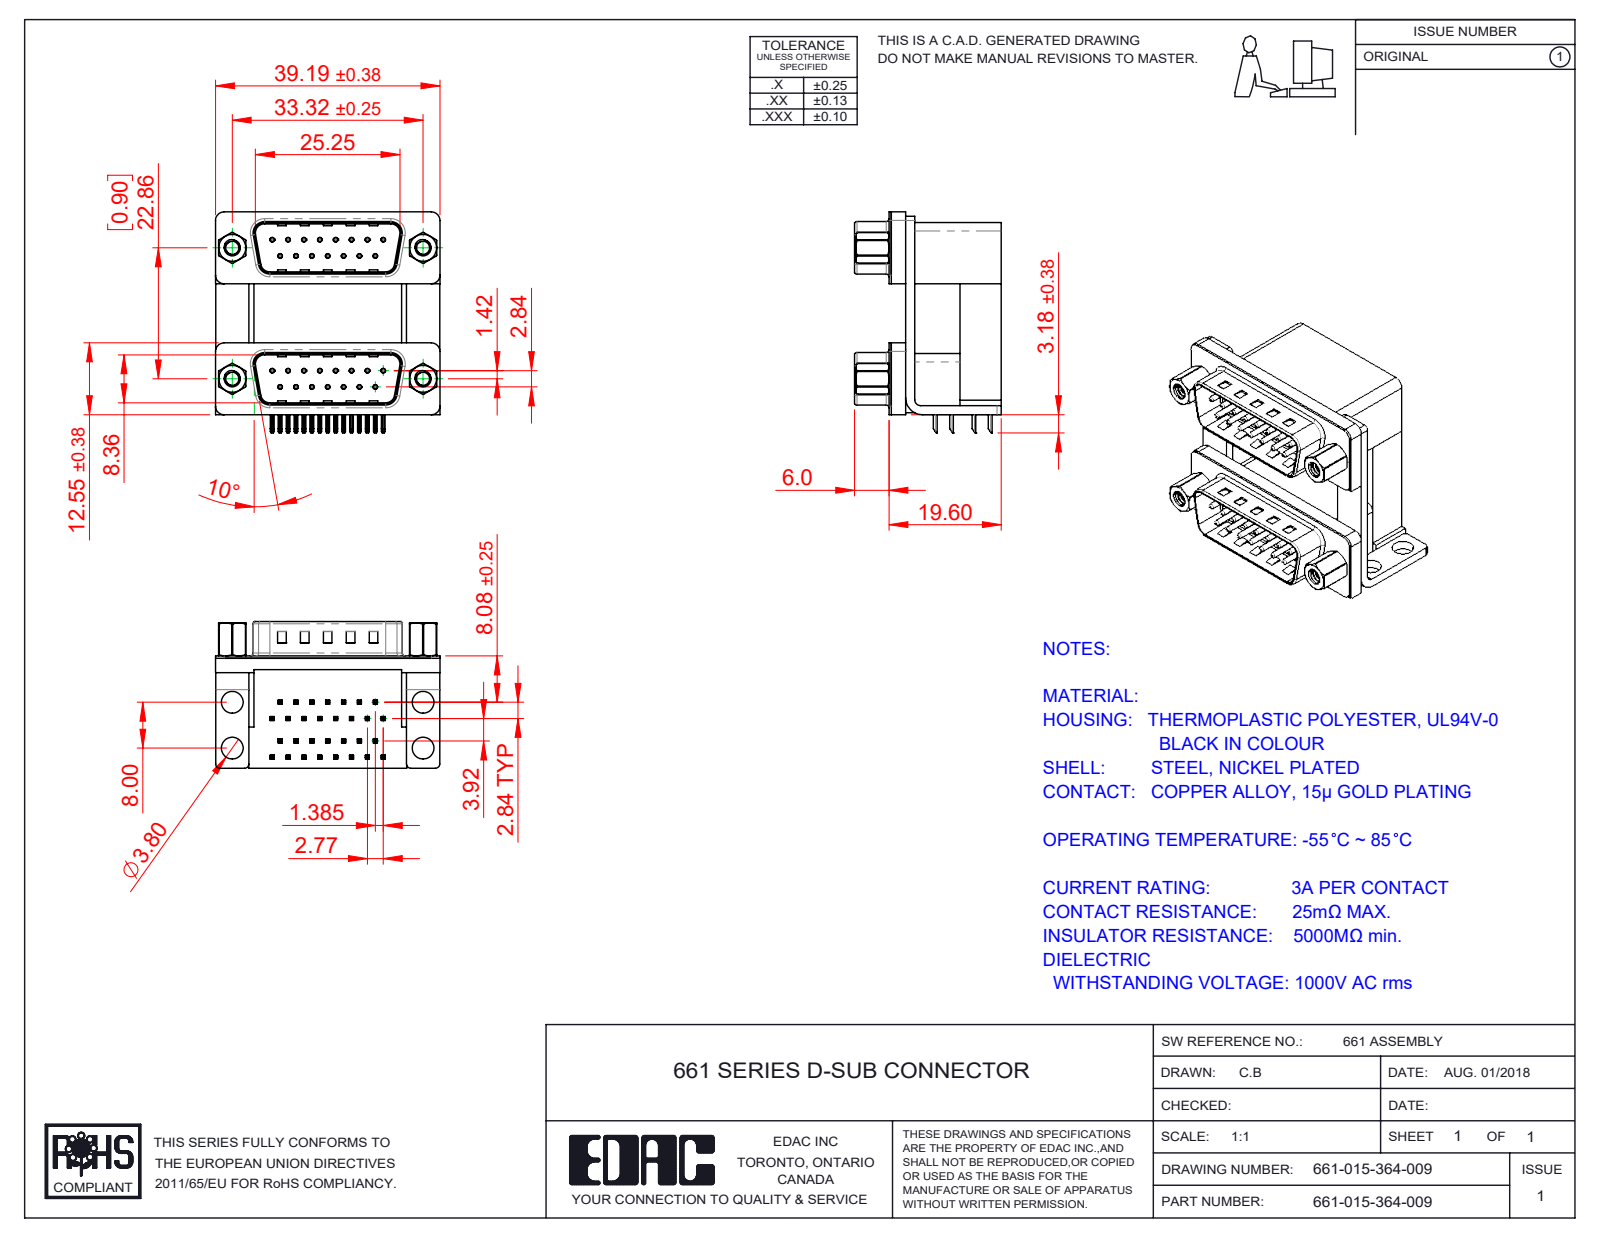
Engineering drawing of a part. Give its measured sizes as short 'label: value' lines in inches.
name: 661 Mounting Bracket_NoneH; 661 Contact Bottom Upper_H; 661-015-364-009; 661 Housing Upper_15 Contacts H (+8 more)
written by: SolidWorks 2020 (CONFIG_CONTROL_DESIGN)
unit: in
bodies: 45 solids, 3214 faces (1878 planar, 998 cylindrical, 338 other)
size: 1.543 × 1.519 × 1.008
volume: 0.95 in³; area: 26.79 in²
holes: 30× ⌀0.014, 30× ⌀0.031, 4× ⌀0.089, 4× ⌀0.09, 4× ⌀0.138, 4× ⌀0.15, 4× ⌀0.157, 4× ⌀0.189, 4× ⌀0.197
bosses: 30× ⌀0.03, 4× ⌀0.193, 4× ⌀0.187, 4× ⌀0.154, 4× ⌀0.11
rounds: 120× R0.01, 60× R0.005, 16× R0.02, 16× R0.059, 8× R0.03, 8× R0.035, 8× R0.063, 8× R0.079
face distances: 0.016, 0.472, 0.9, 0.756, 0.283, 0.657, 0.374, 0.098, 0.488, 0.421
hole spacings: 0.124, 0.109, 0.907, 0.218, 0.926, 0.327, 0.957, 0.9
